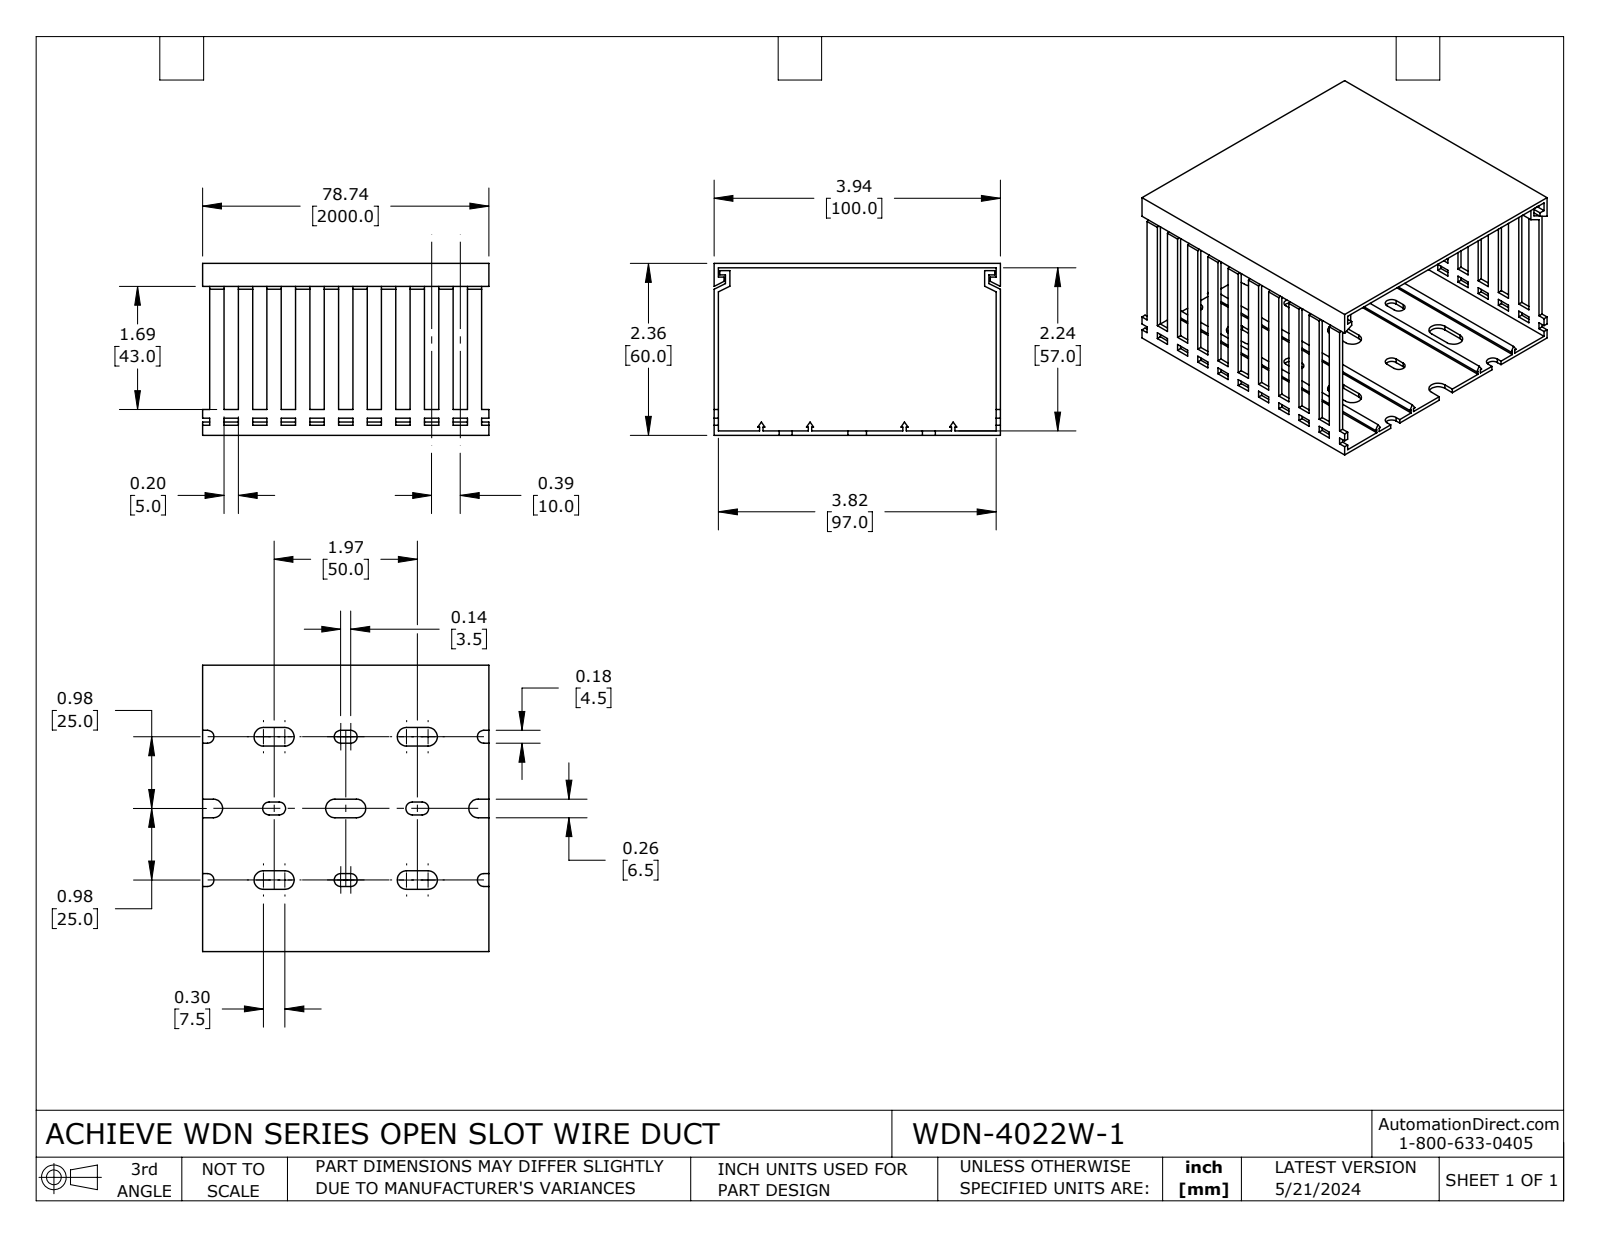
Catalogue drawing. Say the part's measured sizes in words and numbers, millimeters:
The part is named "WDN-4022W-1". Its 3-D file was written by "SolidWorks 2023 (CONFIG_CONTROL_DESIGN)". It is 2 solids with 412 faces: 376 planar, 36 cylindrical and 0 other. Overall it measures 100 by 100 by 60 millimeters. Its volume is 42 980 cubic millimeters and its surface area 63 130 square millimeters. Partial cylindrical surfaces (rounded edges, fillets, slot ends): 12 of radius 2.3, 12 of radius 3.3. The main face-to-face distances are 1.5, 58.5, 60, 57, 98.5, 100, 97, 10, 5, 15.
